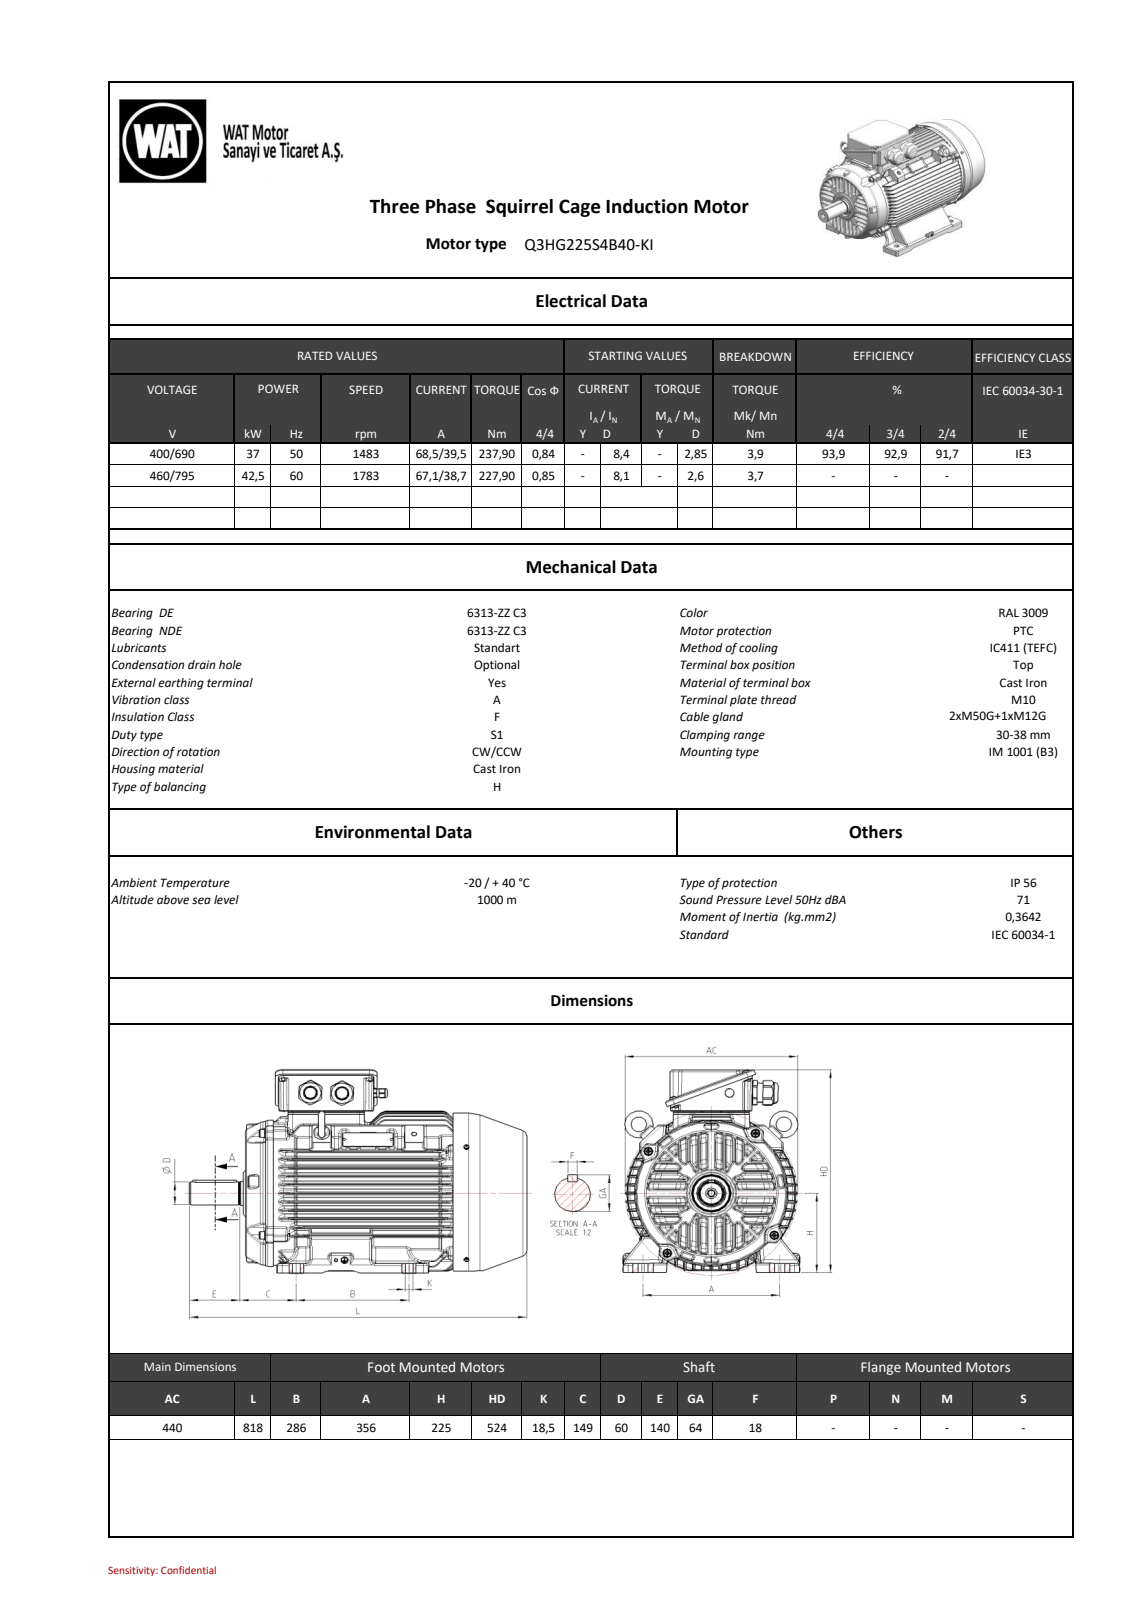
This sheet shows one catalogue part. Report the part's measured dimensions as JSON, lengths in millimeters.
{"part_name": "26000A30F4D8rny2", "step_written_by": "SIEMENS PLM Software NX 11.0 (AUTOMOTIVE_DESIGN)", "units": "millimeters", "bodies": {"solids": 0, "faces": 8452, "planar": 2839, "cylindrical": 1605, "other": 4008}, "overall_size": [818.12, 523.73, 443], "round_holes": [[14, 10], [2.5, 1], [6.8, 1], [10, 1], [17.5, 1], [21, 1], [88.33, 1], [437, 1]], "round_bosses_or_shafts": [[24, 8], [30, 4], [12, 4], [8, 4], [58, 2], [54.8, 2], [35, 2], [440, 1]], "partial_cylinders_radius": [[4, 329], [2, 274], [3, 135], [5, 130], [6, 68], [0.6, 43], [10, 20], [9.25, 12]], "face_to_face_distances": [17.41, 159.69, 17.32, 194.42, 34.89, 142.21, 17.48, 88.37, 52.44, 35.03], "hole_center_spacings": [198, 280.01, 68.76, 227.14, 324.38, 389.98, 396, 127.5]}
